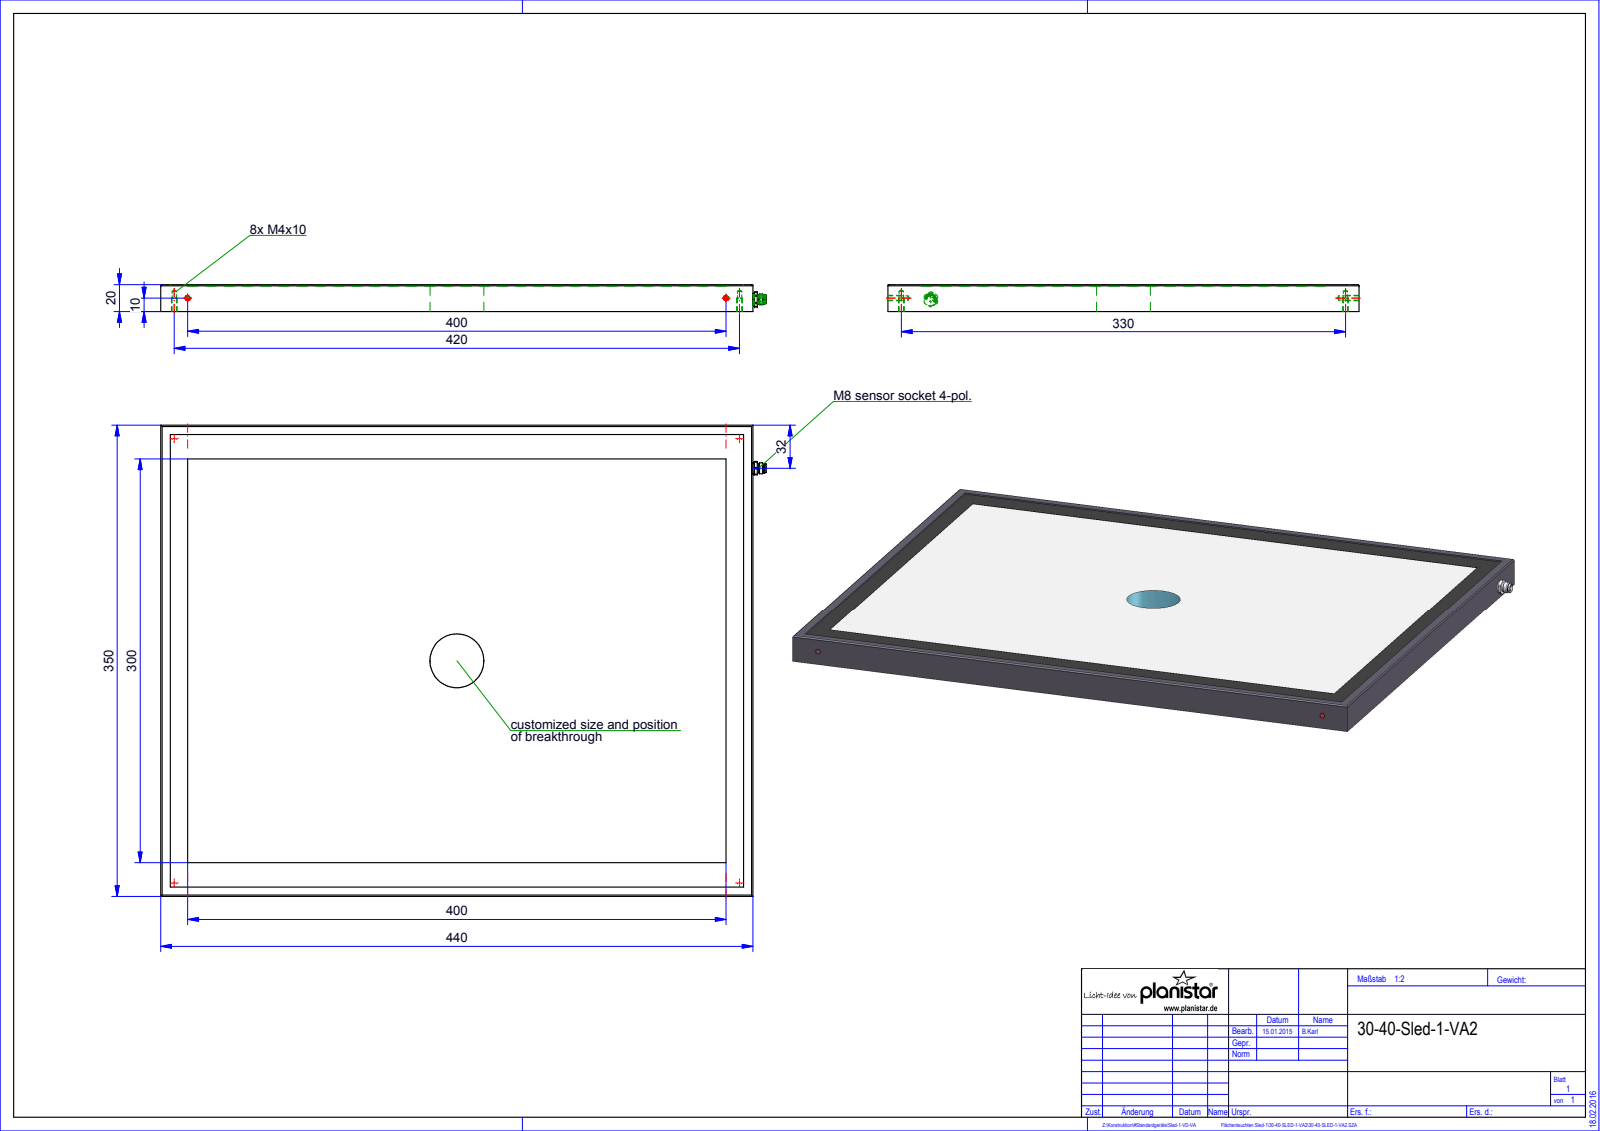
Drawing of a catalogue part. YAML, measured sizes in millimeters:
part_name: "Root; Baugruppe_Xled-2-VD; QUADER_0; 09-3391-00-04"
step_written_by: "HiCAD 2015 2002.1 Build 408 (AUTOMOTIVE_DESIGN)"
units: millimeters
bodies: {solids: 2, faces: 91, planar: 36, cylindrical: 38, other: 17}
overall_size: [449.7, 350, 20]
volume: 2888000
surface_area: 342634
round_holes:
  - {diameter: 3.3, count: 6}
  - {diameter: 4, count: 6}
  - {diameter: 5.8, count: 1}
  - {diameter: 40, count: 1}
round_bosses_or_shafts:
  - {diameter: 1, count: 4}
  - {diameter: 8, count: 1}
  - {diameter: 7.2, count: 1}
  - {diameter: 6.8, count: 1}
  - {diameter: 6.4, count: 1}
partial_cylinders:
  - {radius: 1, count: 4}
  - {radius: 5.5, count: 1}
face_to_face_distances: [18.8, 19, 20, 1.2, 1, 350, 440, 7, 343, 433]
hole_center_spacings: [267.07, 330, 420, 534.13, 400]
